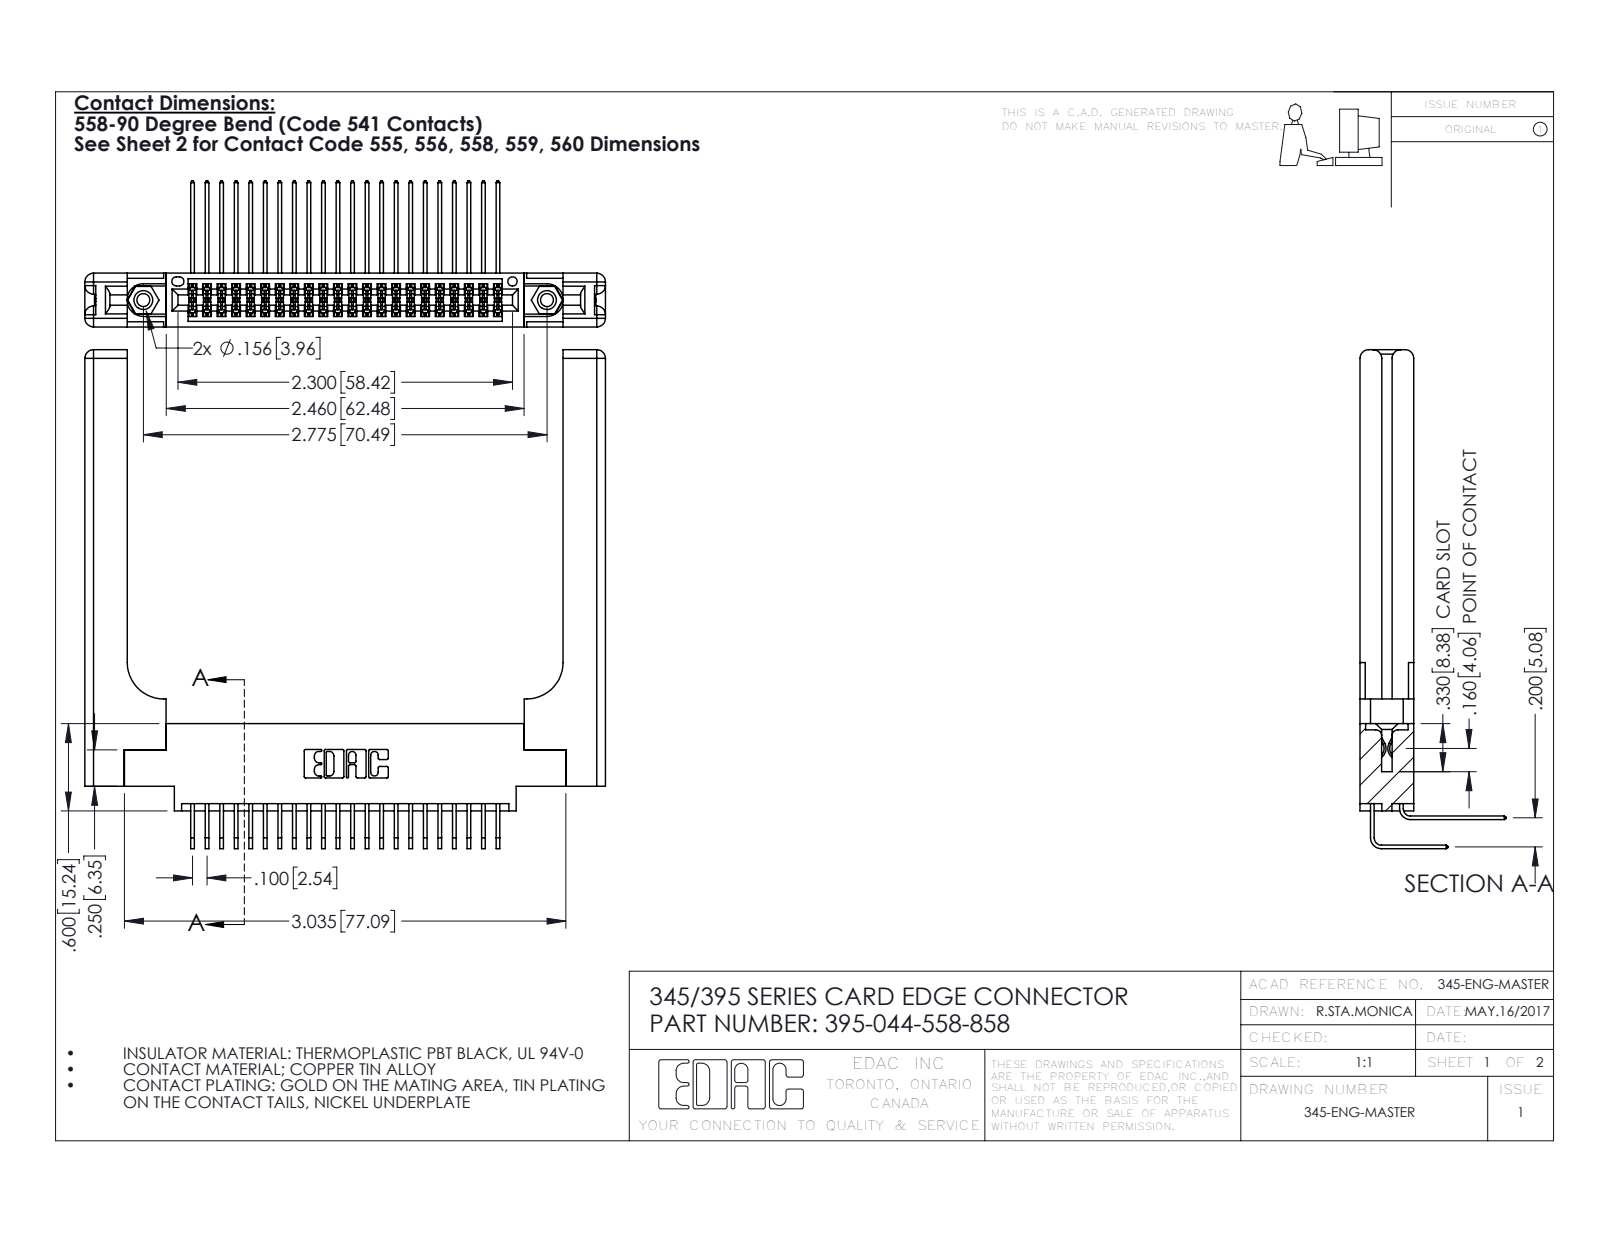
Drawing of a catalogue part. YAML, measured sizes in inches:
part_name: "345-292-001_558 559 Tail - 1; 345 Part_0.170 Offset - 0.156 Dia-TH; 345-292-001_558 Tail - 2; 345-250-001_345-250-001-102 (+2 more)"
step_written_by: "SolidWorks 2016 (CONFIG_CONTROL_DESIGN)"
units: inches
bodies: {solids: 49, faces: 2674, planar: 1772, cylindrical: 842, other: 60}
overall_size: [3.579, 3.429, 1.005]
volume: 1.053
surface_area: 29.44
round_holes:
  - {diameter: 0.089, count: 2}
  - {diameter: 0.125, count: 2}
  - {diameter: 0.156, count: 2}
  - {diameter: 0.064, count: 1}
round_bosses_or_shafts:
  - {diameter: 0.155, count: 2}
partial_cylinders:
  - {radius: 0.006, count: 67}
  - {radius: 0.01, count: 22}
  - {radius: 0.06, count: 16}
  - {radius: 0.007, count: 6}
  - {radius: 0.031, count: 6}
  - {radius: 0.026, count: 3}
  - {radius: 0.014, count: 2}
  - {radius: 0.019, count: 2}
face_to_face_distances: [0.37, 0.072, 0.298, 0.2, 0.15, 0.148, 0.077, 0.098, 0.272, 0.025]
hole_center_spacings: [0.27, 2.541, 2.775]
